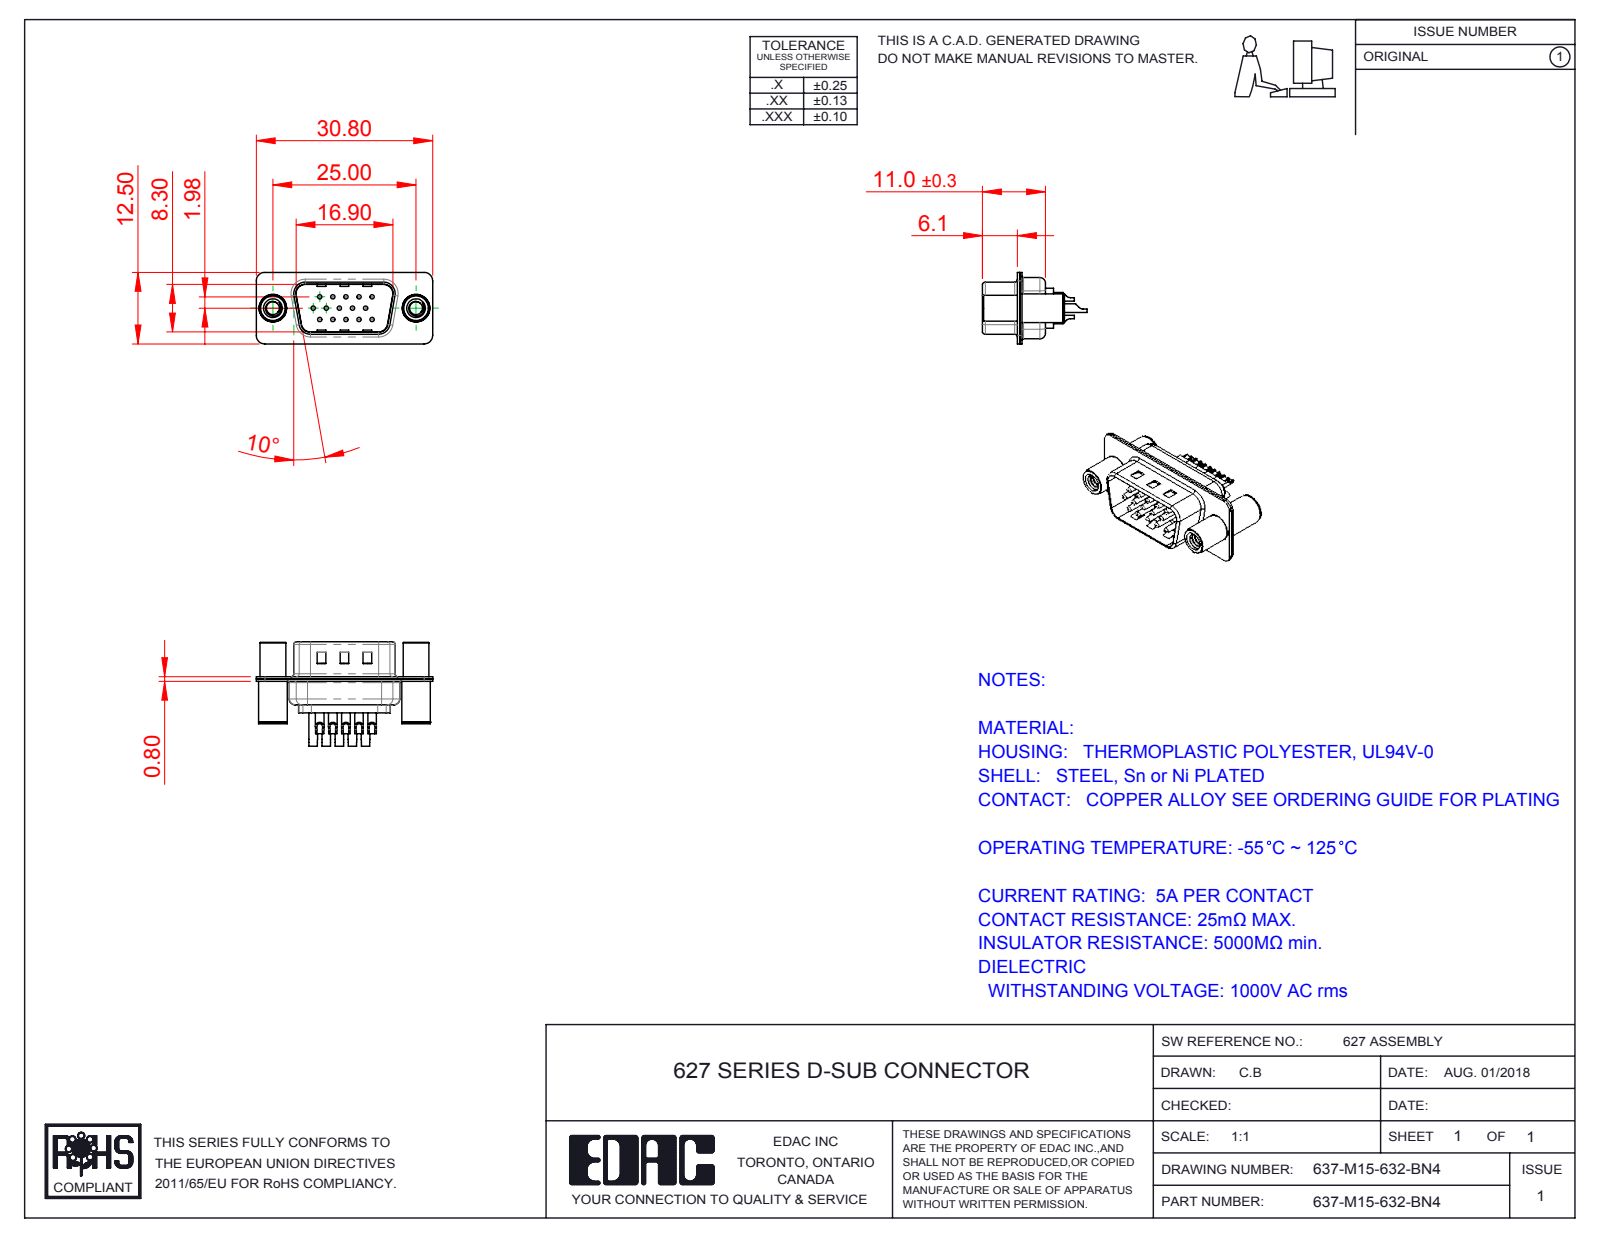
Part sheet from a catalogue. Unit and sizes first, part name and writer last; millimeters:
Units: millimetres
Overall size (bounding box): 30.8 × 18.25 × 12.5
Round holes (diameter × count): ⌀0.75 ×15, ⌀1 ×15, ⌀1.6 ×15, ⌀2 ×15, ⌀2.26 ×2, ⌀3.26 ×2, ⌀4 ×2, ⌀4.8 ×2
Round bosses / shafts (diameter × count): ⌀1.5 ×15, ⌀5 ×2, ⌀4.9 ×2, ⌀4.5 ×2
Partial cylindrical surfaces — rounded edges, fillets, slot ends (radius × count): R1.5 ×16, R2 ×12, R0.5 ×8, R1.6 ×8, R1 ×7, R0.25 ×4, R0.6 ×4, R0.65 ×4
Main face-to-face distances: 0.4, 0.8, 9.5, 9.1, 0.65, 8.7, 9.9, 0.75, 0.35, 1.2
Hole centre spacings: 3.96, 2.28, 2.29, 4.57, 6.05, 6.86, 7.92, 6.04
Volume: 1 685 mm³ · Surface area: 4 805 mm²
Bodies: 20 solids, 945 faces (248 planar, 421 cylindrical, 276 other)
Part name (STEP PRODUCT): 637M Shell Rear_15 Contacts; 637M Contact Row 2_32; 637M Contact Row 1_32; 637M 4-40 Threaded Standoff and Board Spacer (+4 more)
STEP written by: SolidWorks 2016 (CONFIG_CONTROL_DESIGN)
